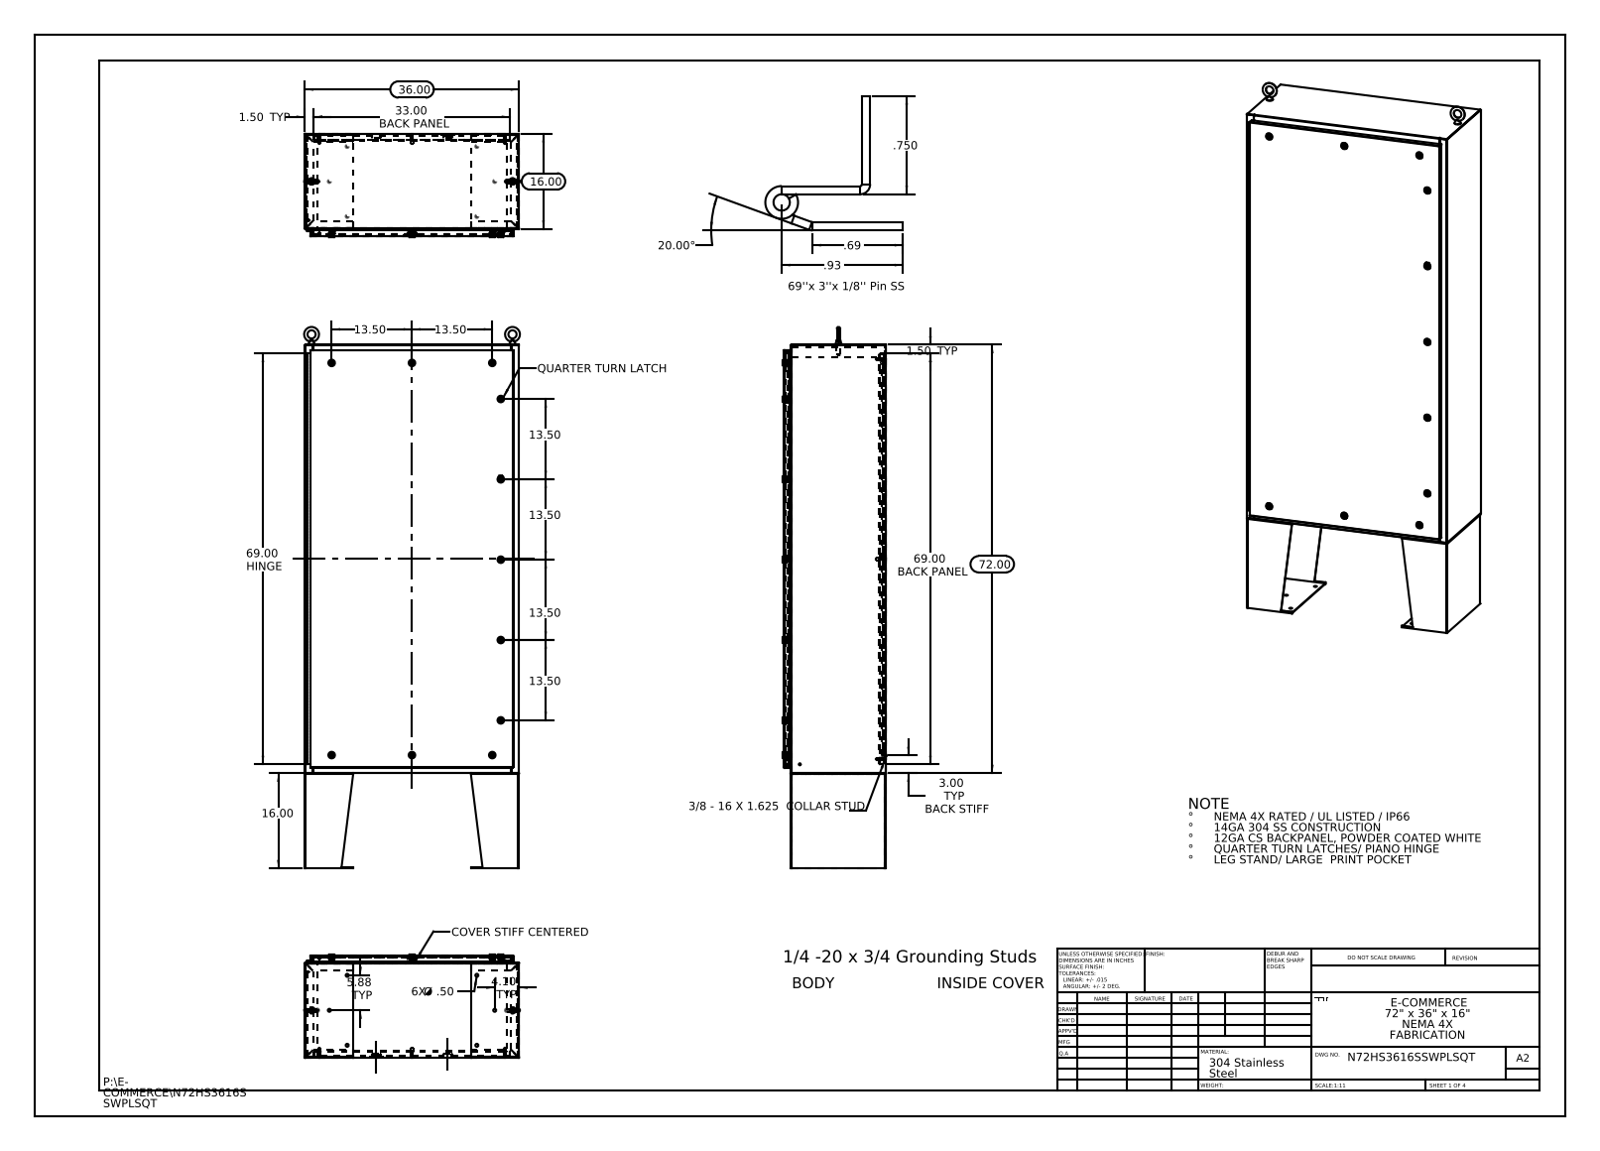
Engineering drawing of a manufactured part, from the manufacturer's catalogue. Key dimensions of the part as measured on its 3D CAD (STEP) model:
Part name (STEP PRODUCT): HW-EYE-NH-20425_3014T52; N72HS3616SSWPLSQT SD-LSK-Stand; N72HS3616SSWPLSQT Mounting Studs; N72HS3616SSWPLSQT SD-LSK-ASSY (+8 more)
STEP written by: SolidWorks 2013 (CONFIG_CONTROL_DESIGN)
Units: inches
Bodies: 36 solids, 2637 faces (1327 planar, 1114 cylindrical, 196 other)
Overall size (bounding box): 91 × 36.271 × 17.201
Volume: 1 149 in³ · Surface area: 27 806 in²
Round holes (diameter × count): ⌀0.5 ×14, ⌀0.25 ×8, ⌀0.75 ×4, ⌀0.125 ×1, ⌀0.125 ×1
Round bosses / shafts (diameter × count): ⌀0.625 ×10, ⌀0.375 ×8, ⌀0.33 ×8, ⌀0.157 ×8, ⌀0.14 ×8, ⌀0.315 ×2, ⌀0.236 ×2, ⌀0.25 ×1
Partial cylindrical surfaces — rounded edges, fillets, slot ends (radius × count): R0.013 ×36, R0.088 ×30, R0.039 ×8, R0.143 ×8, R0.019 ×6, R0.442 ×6, R0.117 ×4, R0.125 ×4
Main face-to-face distances: 0.075, 17.126, 0.104, 17.051, 1.075, 17.201, 35.925, 16.126, 1, 16.051
Hole centre spacings: 2.225, 8.393, 25.48, 28.397, 33.625, 37.078, 45.904, 69.041
